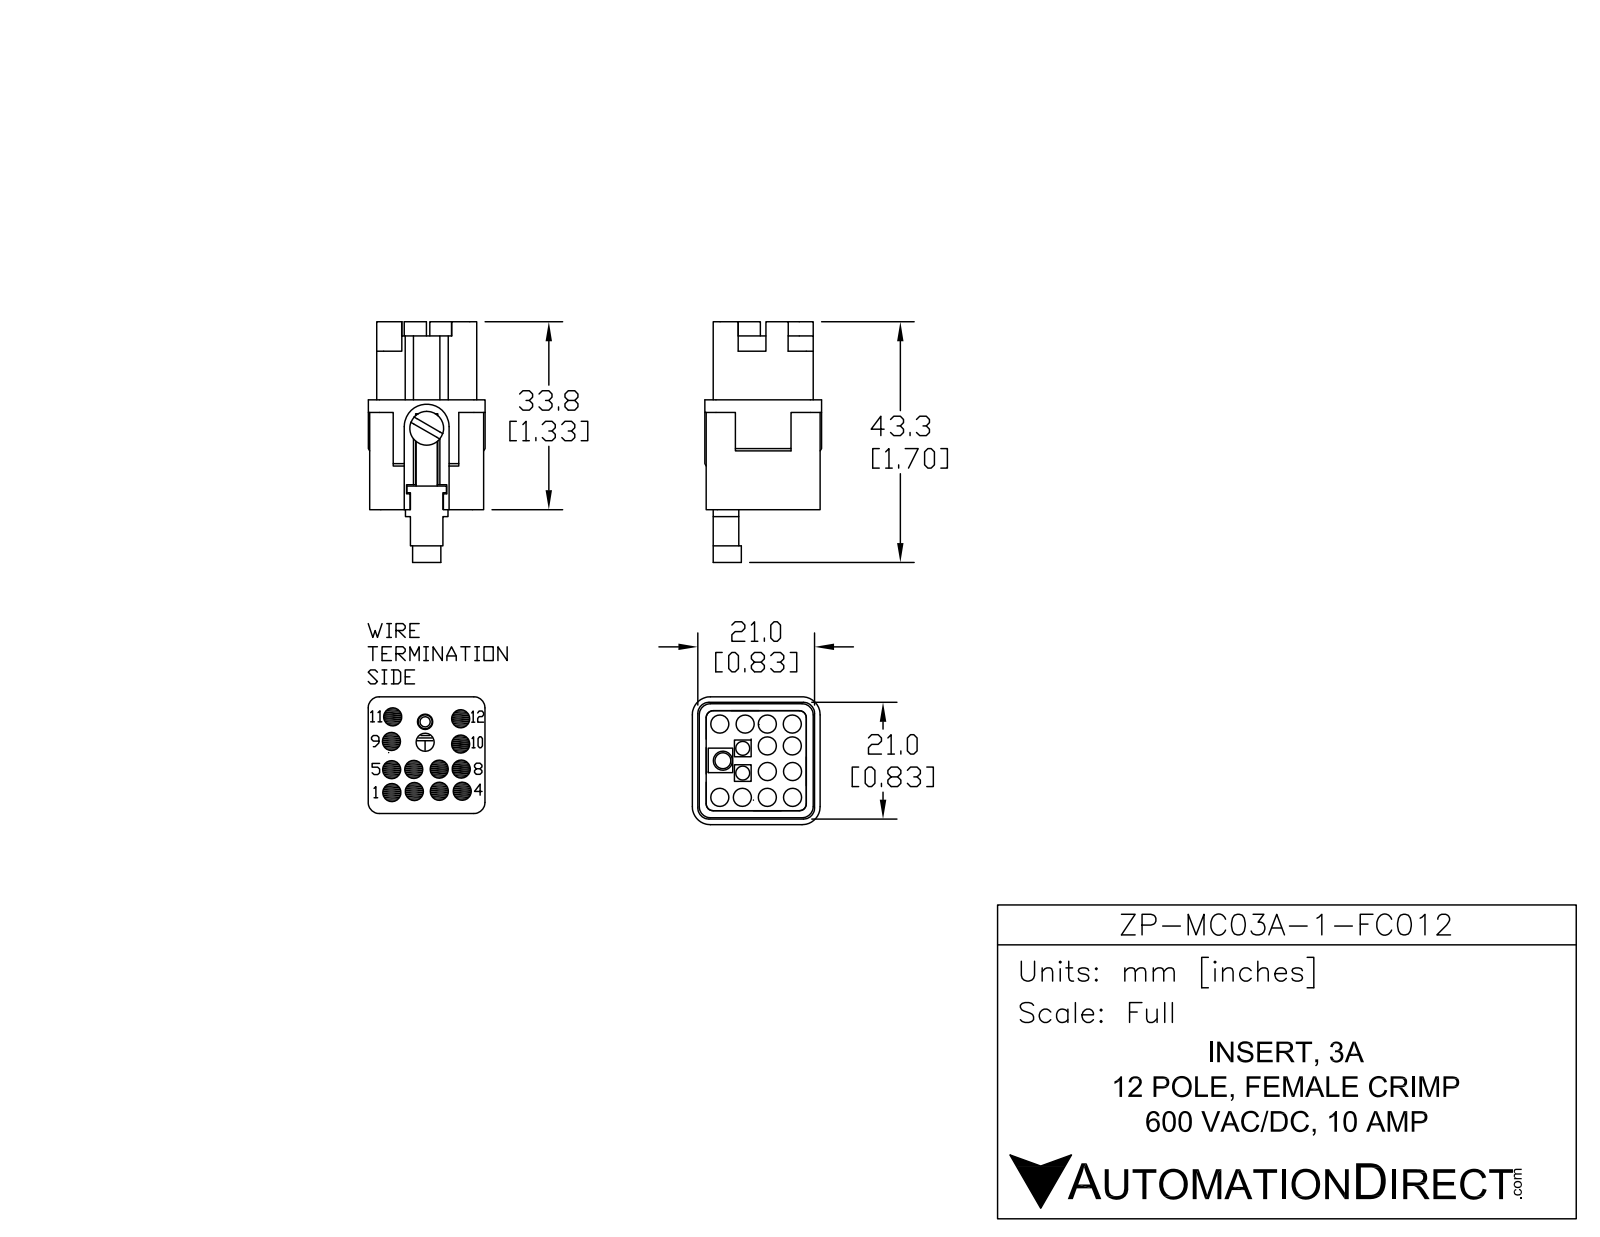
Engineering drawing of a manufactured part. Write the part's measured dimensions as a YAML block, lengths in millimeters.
part_name: "ZP-MC03A-1-FC012"
step_written_by: "SolidWorks 2014 (AUTOMOTIVE_DESIGN)"
units: millimeters
bodies: {solids: 3, faces: 240, planar: 159, cylindrical: 76, other: 5}
overall_size: [43.3, 21, 21]
volume: 8280
surface_area: 9043
round_holes:
  - {diameter: 3.25, count: 13}
  - {diameter: 2.5, count: 2}
  - {diameter: 1.83, count: 1}
  - {diameter: 2.75, count: 1}
  - {diameter: 3.64, count: 1}
  - {diameter: 4, count: 1}
round_bosses_or_shafts:
  - {diameter: 5.08, count: 1}
  - {diameter: 4, count: 1}
  - {diameter: 2.5, count: 1}
partial_cylinders:
  - {radius: 2, count: 13}
  - {radius: 1.25, count: 4}
  - {radius: 1, count: 2}
  - {radius: 1.89, count: 2}
  - {radius: 2, count: 2}
  - {radius: 2.5, count: 2}
  - {radius: 2.53, count: 1}
  - {radius: 4.03, count: 1}
face_to_face_distances: [19.25, 1.25, 3, 18, 1.5, 19.5, 20.75, 20.5, 4.44, 21]
hole_center_spacings: [9.04, 9.55, 3.97, 4.21, 4.61, 5.61, 5.87, 6.4]
